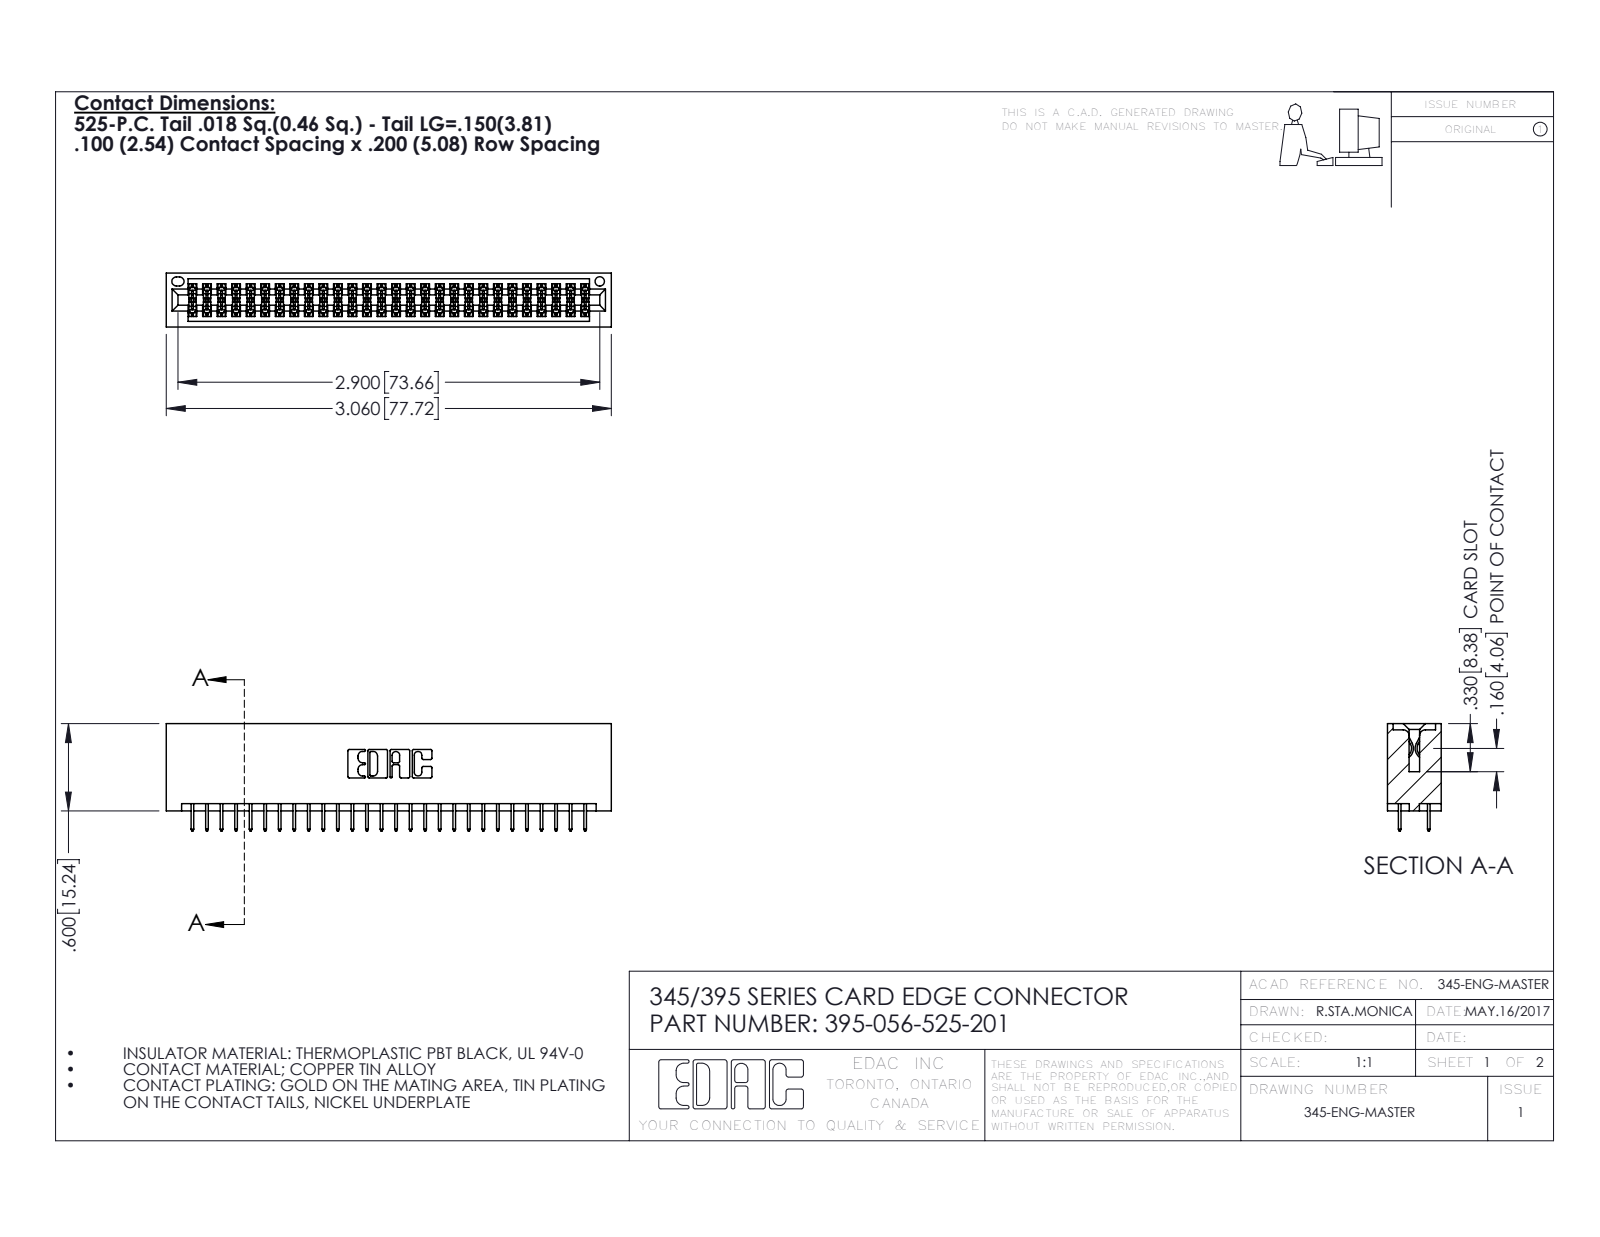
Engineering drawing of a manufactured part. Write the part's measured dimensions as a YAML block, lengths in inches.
part_name: "345-292-001_345-293-125; 345 Part_No Mounting Lugs; 395-056-525-201"
step_written_by: "SolidWorks 2020 (CONFIG_CONTROL_DESIGN)"
units: inches
bodies: {solids: 57, faces: 3142, planar: 2260, cylindrical: 882, other: 0}
overall_size: [3.06, 0.737, 0.37]
volume: 0.485
surface_area: 17.82
round_holes:
  - {diameter: 0.064, count: 1}
partial_cylinders:
  - {radius: 0.006, count: 112}
  - {radius: 0.01, count: 22}
  - {radius: 0.007, count: 6}
  - {radius: 0.031, count: 6}
  - {radius: 0.026, count: 3}
  - {radius: 0.014, count: 2}
  - {radius: 0.019, count: 2}
  - {radius: 0.022, count: 2}
face_to_face_distances: [0.298, 0.072, 0.2, 0.37, 0.098, 0.272, 0.025, 0.225, 0.072, 0.175]
